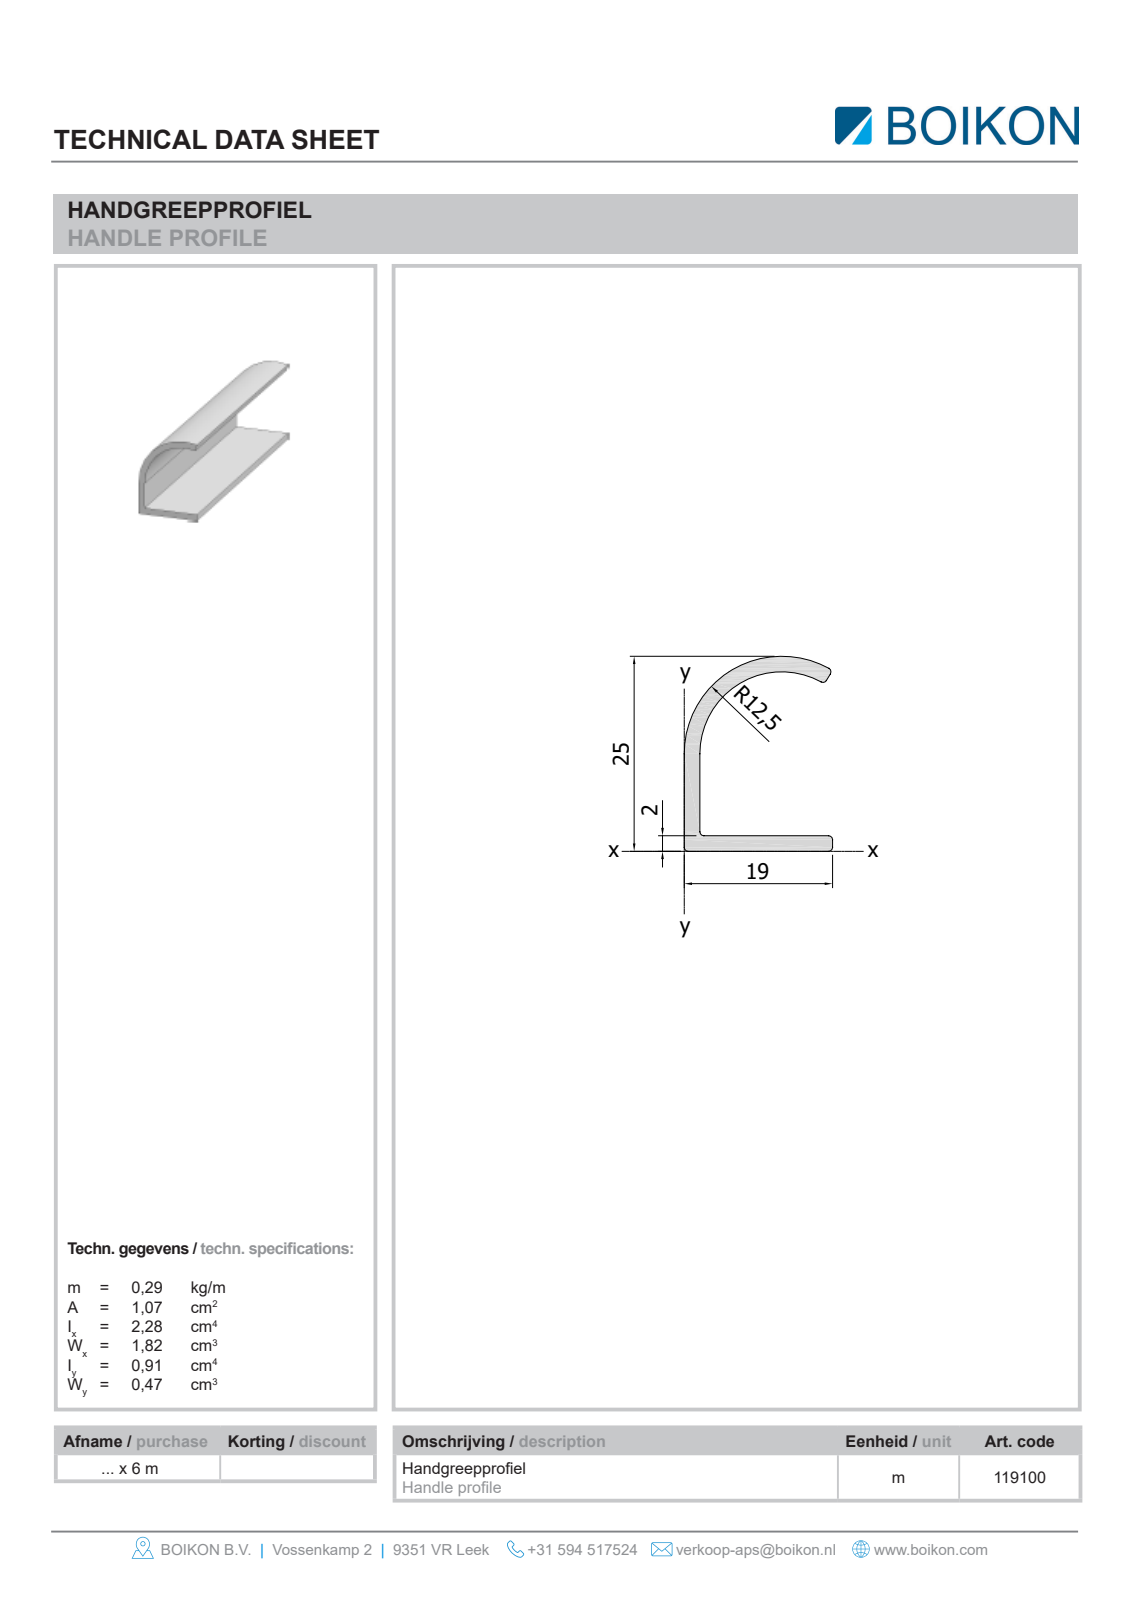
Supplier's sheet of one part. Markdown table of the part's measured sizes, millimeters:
| quantity | value |
| --- | --- |
| part name | Root; 119100HandgreepprofielBOIKON0 |
| STEP written by | HiCAD 2013 1802.4 Build 509 (AUTOMOTIVE_DESIGN) |
| units | millimeters |
| bodies | 1 solid, 10 faces (8 planar, 2 cylindrical, 0 other) |
| overall size | 1000 × 25 × 19 |
| volume | 105 540 mm³ |
| surface area | 109 752 mm² |
| partial cylindrical surfaces (radius × count) | 13 × 1, 15 × 1 |
| main face-to-face distances | 2, 17, 19, 1000 |
